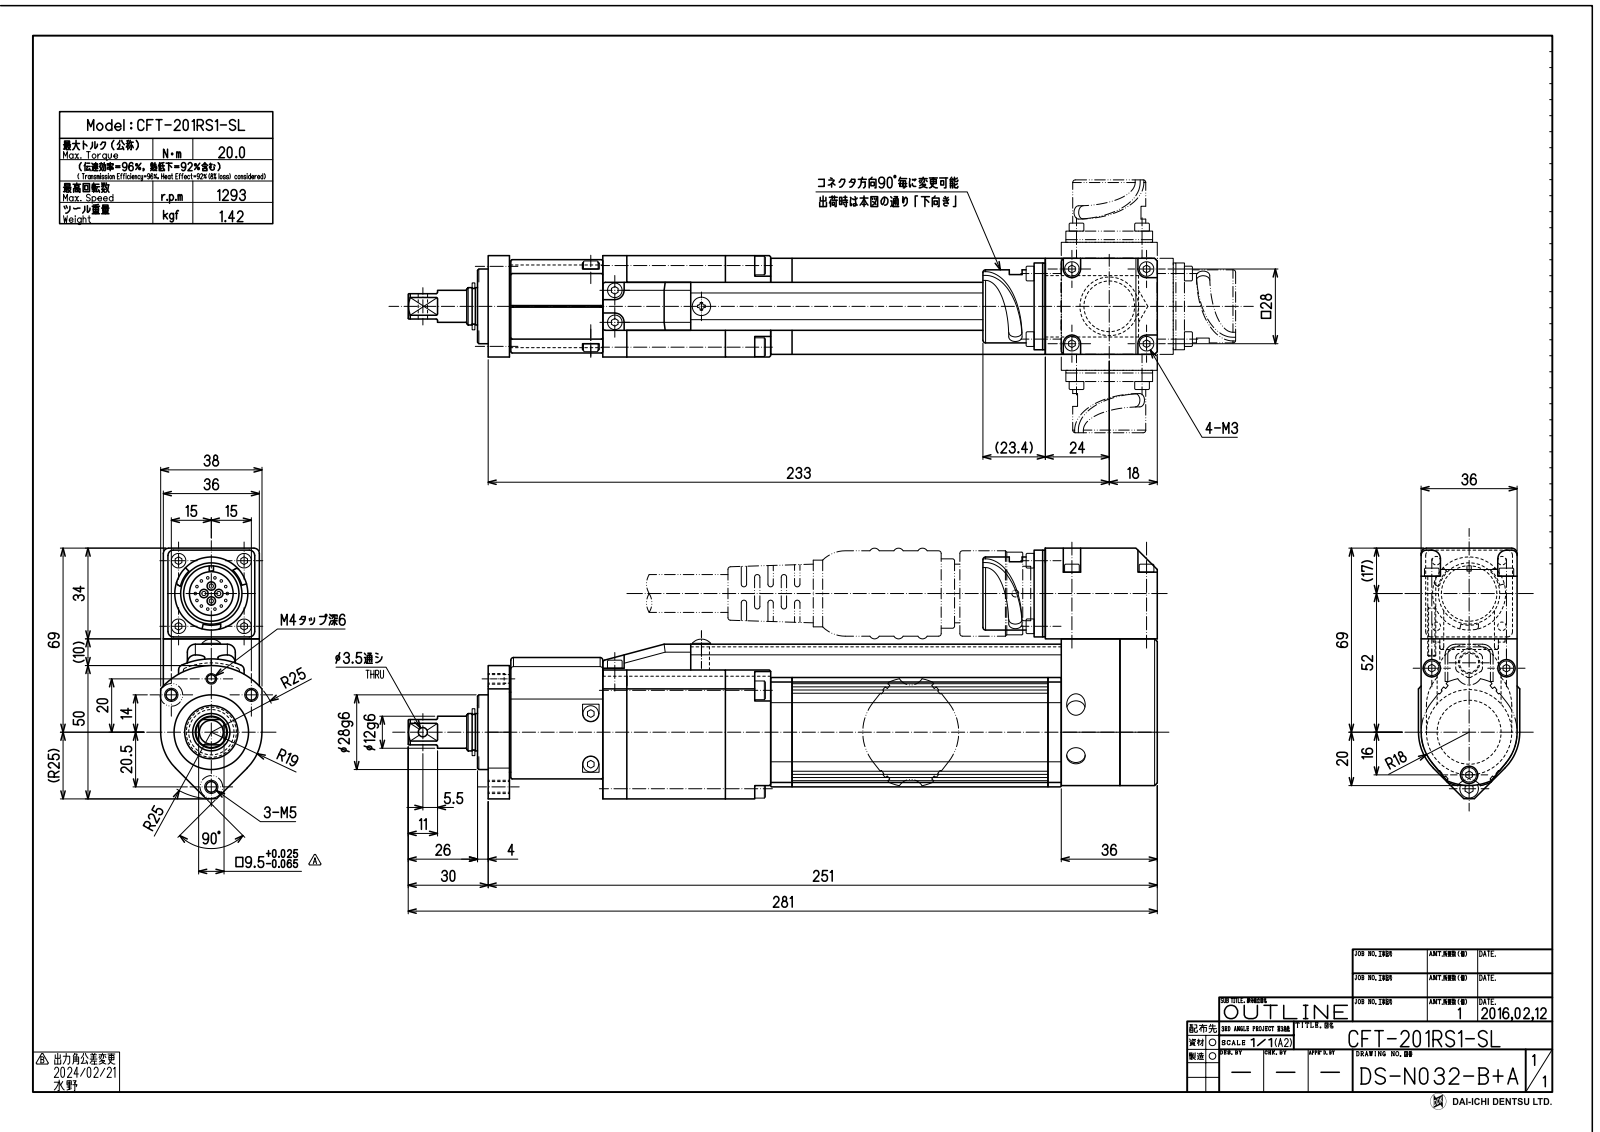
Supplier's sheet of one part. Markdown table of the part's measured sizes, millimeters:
| quantity | value |
| --- | --- |
| part name | CFT-201RS1-SL |
| STEP written by | SolidWorks 2015 (CONFIG_CONTROL_DESIGN) |
| units | millimeters |
| bodies | 30 solids, 431 faces (214 planar, 138 cylindrical, 79 other) |
| overall size | 281 × 94 × 38 |
| volume | 421 924 mm³ |
| surface area | 94 856 mm² |
| round holes (diameter × count) | 4.2 × 3, 3.3 × 1, 3.5 × 1, 20.4 × 1 |
| round bosses / shafts (diameter × count) | 5.5 × 10, 7 × 4, 28 × 1, 27.4 × 1, 17.6 × 1, 14 × 1, 13.4 × 1, 12 × 1 |
| partial cylindrical surfaces (radius × count) | 3 × 6, 1 × 5, 3.25 × 4, 20.5 × 4, 5 × 3, 2 × 2, 3.5 × 2, 18.8 × 2 |
| main face-to-face distances | 36, 18, 9, 1, 37, 8, 106, 23, 27, 5 |
| hole center spacings | 16.16, 37.62, 40.85, 30, 32, 40.5, 72.5 |
